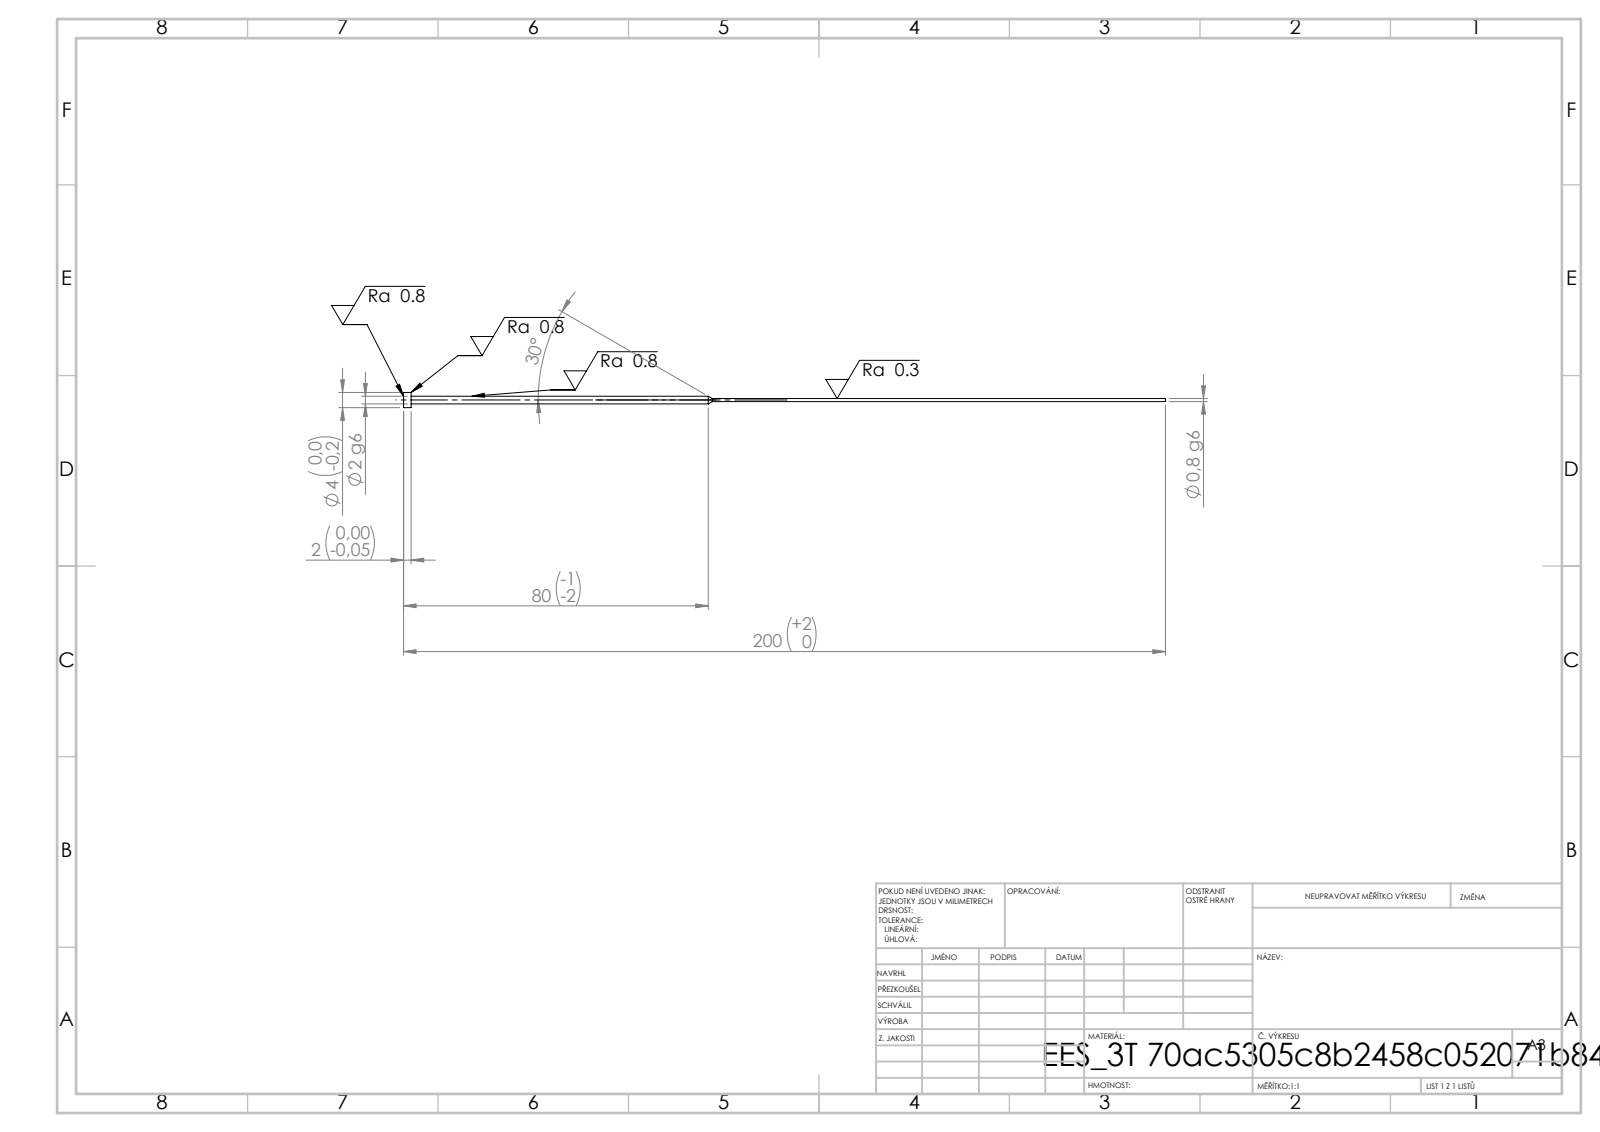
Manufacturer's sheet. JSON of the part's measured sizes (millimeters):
{"step_written_by": "SolidWorks 2019 (CONFIG_CONTROL_DESIGN)", "units": "millimeters", "bodies": {"solids": 1, "faces": 11, "planar": 3, "cylindrical": 6, "other": 2}, "overall_size": [200, 4, 4], "volume_mm3": 332, "surface_area_mm2": 842, "round_bosses_or_shafts": [[4, 1], [2, 1], [0.8, 1]], "face_to_face_distances": [2, 198, 200]}
